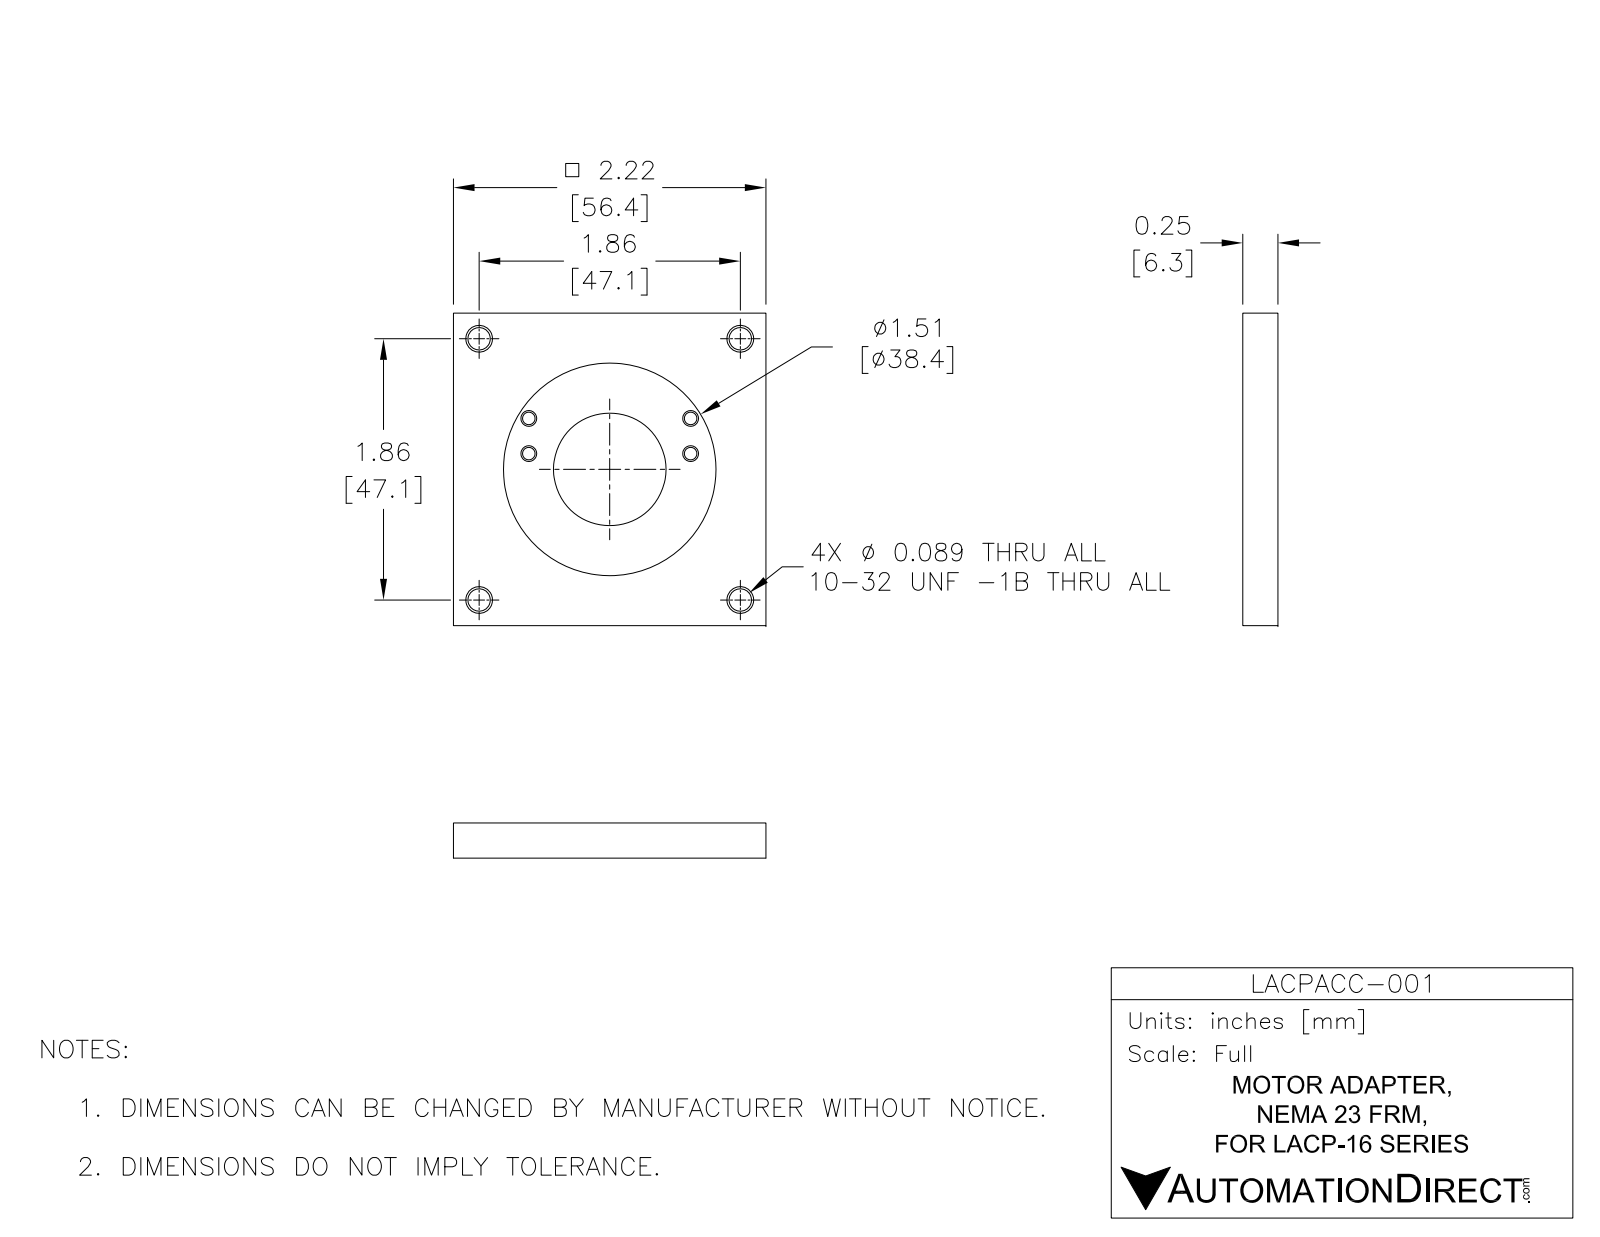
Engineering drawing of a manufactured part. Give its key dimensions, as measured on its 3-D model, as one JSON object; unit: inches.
{"part_name": "LACPACC-001", "step_written_by": "SolidWorks 2015 (AUTOMOTIVE_DESIGN)", "units": "inches", "bodies": {"solids": 1, "faces": 27, "planar": 7, "cylindrical": 20, "other": 0}, "overall_size": [2.22, 2.22, 0.25], "volume_in3": 0.955, "surface_area_in2": 12.39, "round_holes": [[0.089, 4], [0.159, 4], [0.8, 1], [1.51, 1]], "face_to_face_distances": [0.25, 0.15, 0.1, 2.22], "hole_center_spacings": [1.312, 1.856, 0.25, 0.667, 0.679, 1.098, 1.337, 1.606]}
